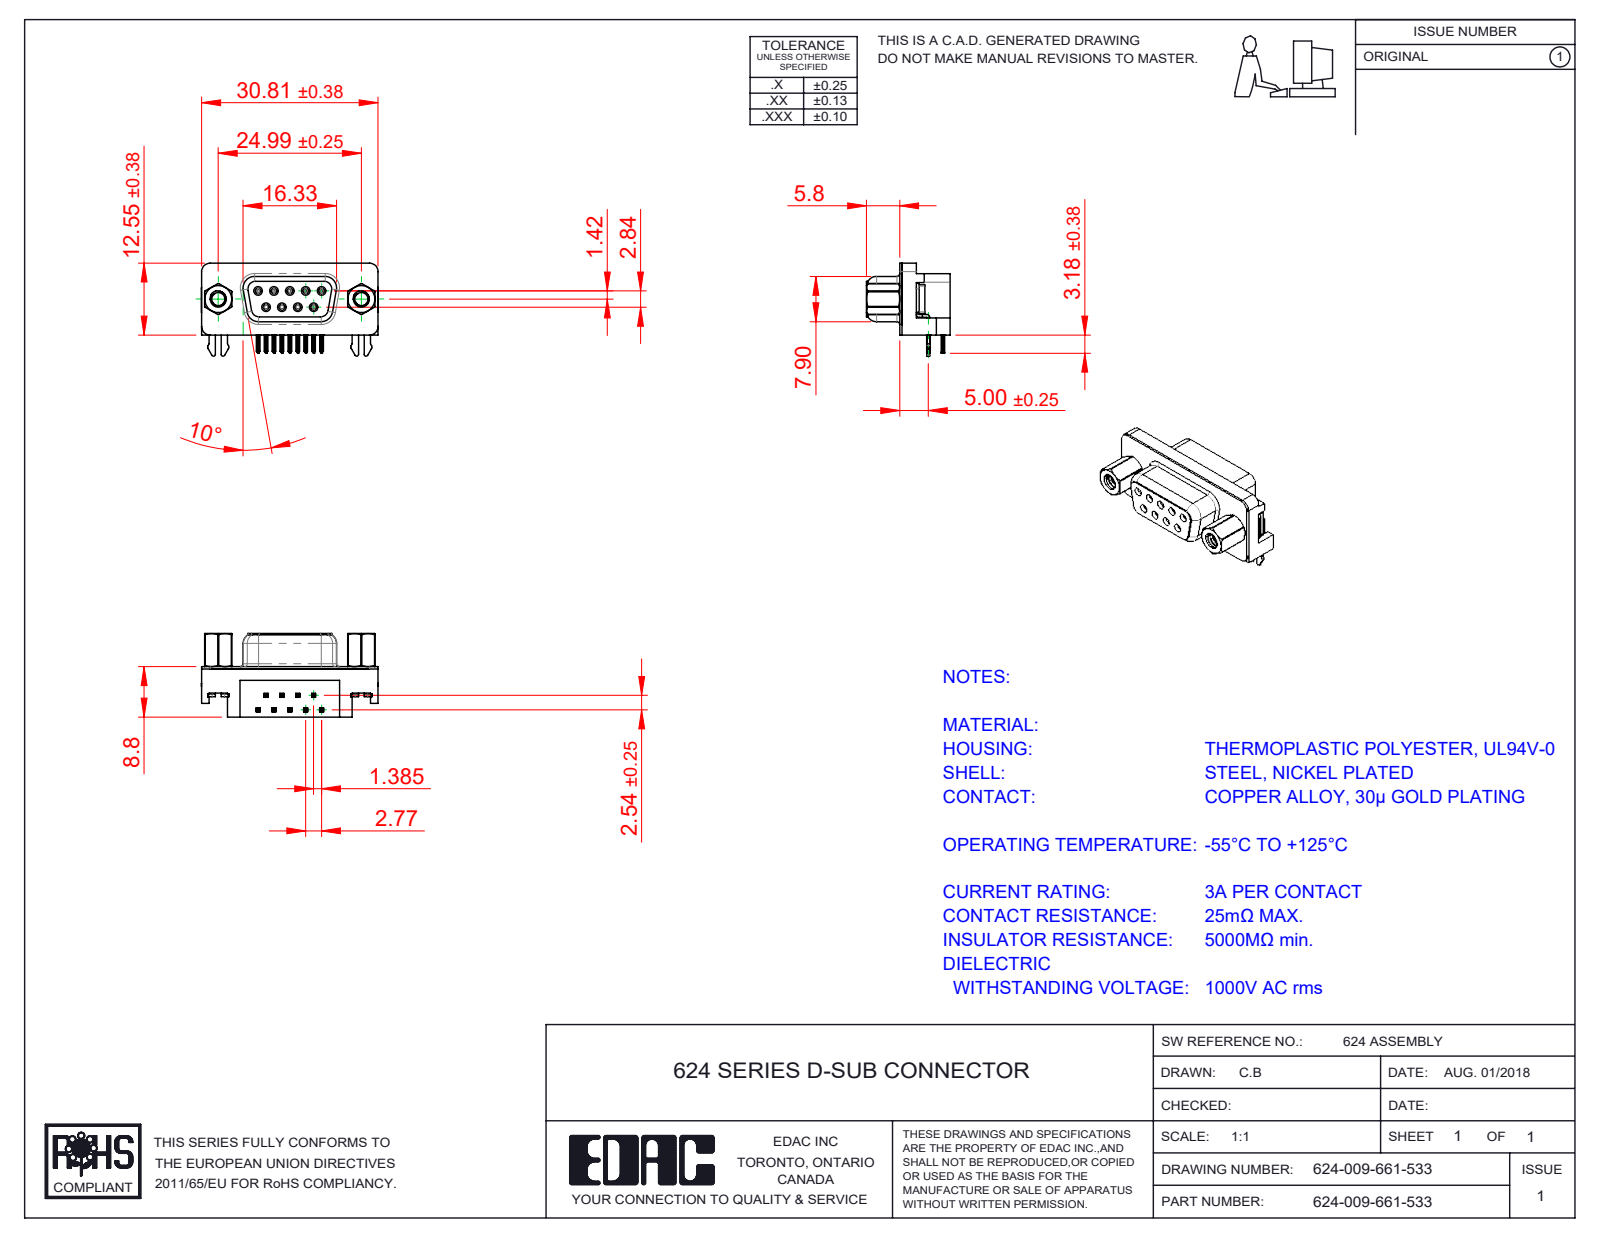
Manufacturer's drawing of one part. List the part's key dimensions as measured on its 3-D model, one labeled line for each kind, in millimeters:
Part name (STEP PRODUCT): 624 2 Prong Board Lock; 624 4-40 Threaded Rivet; 624 4-40 Hex Standoff 5; 624-009-661-533 (+4 more)
STEP written by: SolidWorks 2016 (CONFIG_CONTROL_DESIGN)
Units: millimetres
Bodies: 17 solids, 1676 faces (692 planar, 478 cylindrical, 506 other)
Overall size (bounding box): 30.89 × 16.25 × 14.6
Volume: 3 155 mm³ · Surface area: 4 867 mm²
Round holes (diameter × count): ⌀0.8 ×9, ⌀0.9 ×9, ⌀2.26 ×2, ⌀2.29 ×2, ⌀4 ×2, ⌀4.8 ×2, ⌀5 ×2
Round bosses / shafts (diameter × count): ⌀1.2 ×9, ⌀4.9 ×2, ⌀4.75 ×2, ⌀3.9 ×2, ⌀2.79 ×2
Partial cylindrical surfaces — rounded edges, fillets, slot ends (radius × count): R0.1 ×72, R0.15 ×36, R0.35 ×18, R0.5 ×10, R1 ×10, R0.34 ×9, R0.25 ×8, R1.35 ×8
Main face-to-face distances: 0.4, 8.4, 8.8, 2.9, 6.2, 2.5, 5.9, 0.35, 0.85, 10.69
Hole centre spacings: 3.16, 2.77, 5.54, 5.03, 5.04, 8.31, 7.48, 7.49
